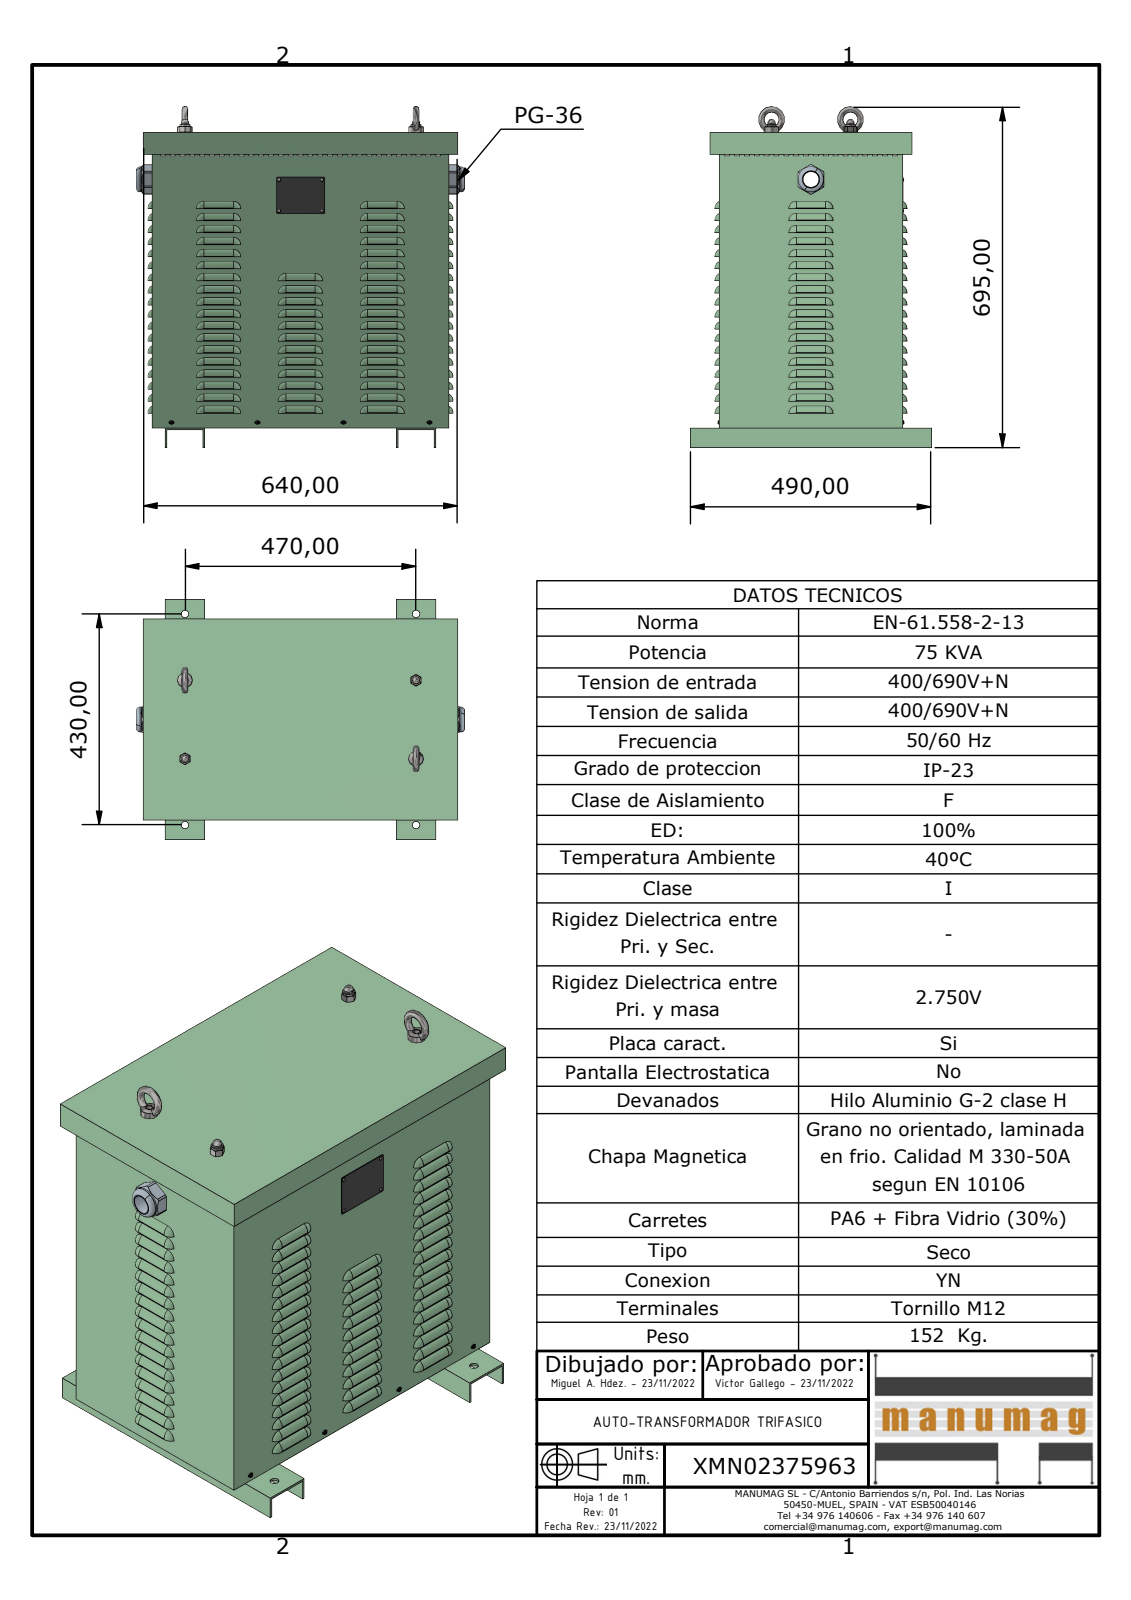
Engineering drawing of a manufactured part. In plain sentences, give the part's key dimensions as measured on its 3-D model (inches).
The part is named "XMN02375963; JE060 - JE075 CUERPO; JE060 - JE075 BASE; JE060 - JE075 PATAS (+7 more)". Its 3-D file was written by "Autodesk Inventor 2023 (AUTOMOTIVE_DESIGN)". It is 24 solids with 2907 faces: 1145 planar, 1024 cylindrical and 738 other. Overall it measures 27.362 by 26.307 by 19.291 inches. Its volume is 281.6 cubic inches and its surface area 6 273 square inches. Round holes: 364 of diameter 0.433, 8 of diameter 0.591, 4 of diameter 0.157, 4 of diameter 0.197, 2 of diameter 0.398, 2 of diameter 0.466, 1 of diameter 1.26, 1 of diameter 1.89. Round bosses or shafts: 4 of diameter 0.157, 4 of diameter 0.143, 4 of diameter 0.126, 2 of diameter 2.012, 2 of diameter 1.181, 2 of diameter 0.827, 2 of diameter 0.614, 1 of diameter 1.868. Partial cylindrical surfaces (rounded edges, fillets, slot ends): 132 of radius 0.551, 72 of radius 0.276, 72 of radius 0.591, 12 of radius 0.153, 8 of radius 0.098, 4 of radius 0.079, 4 of radius 0.295, 2 of radius 1.181. The main face-to-face distances are 0.079, 14.567, 23.622, 23.661, 14.488, 14.646, 23.701, 23.583, 23.543, 23.74. The hole center spacings are 1.181, 0.835, 5.074, 5.197, 5.787, 6.841, 10.984, 4.606.
